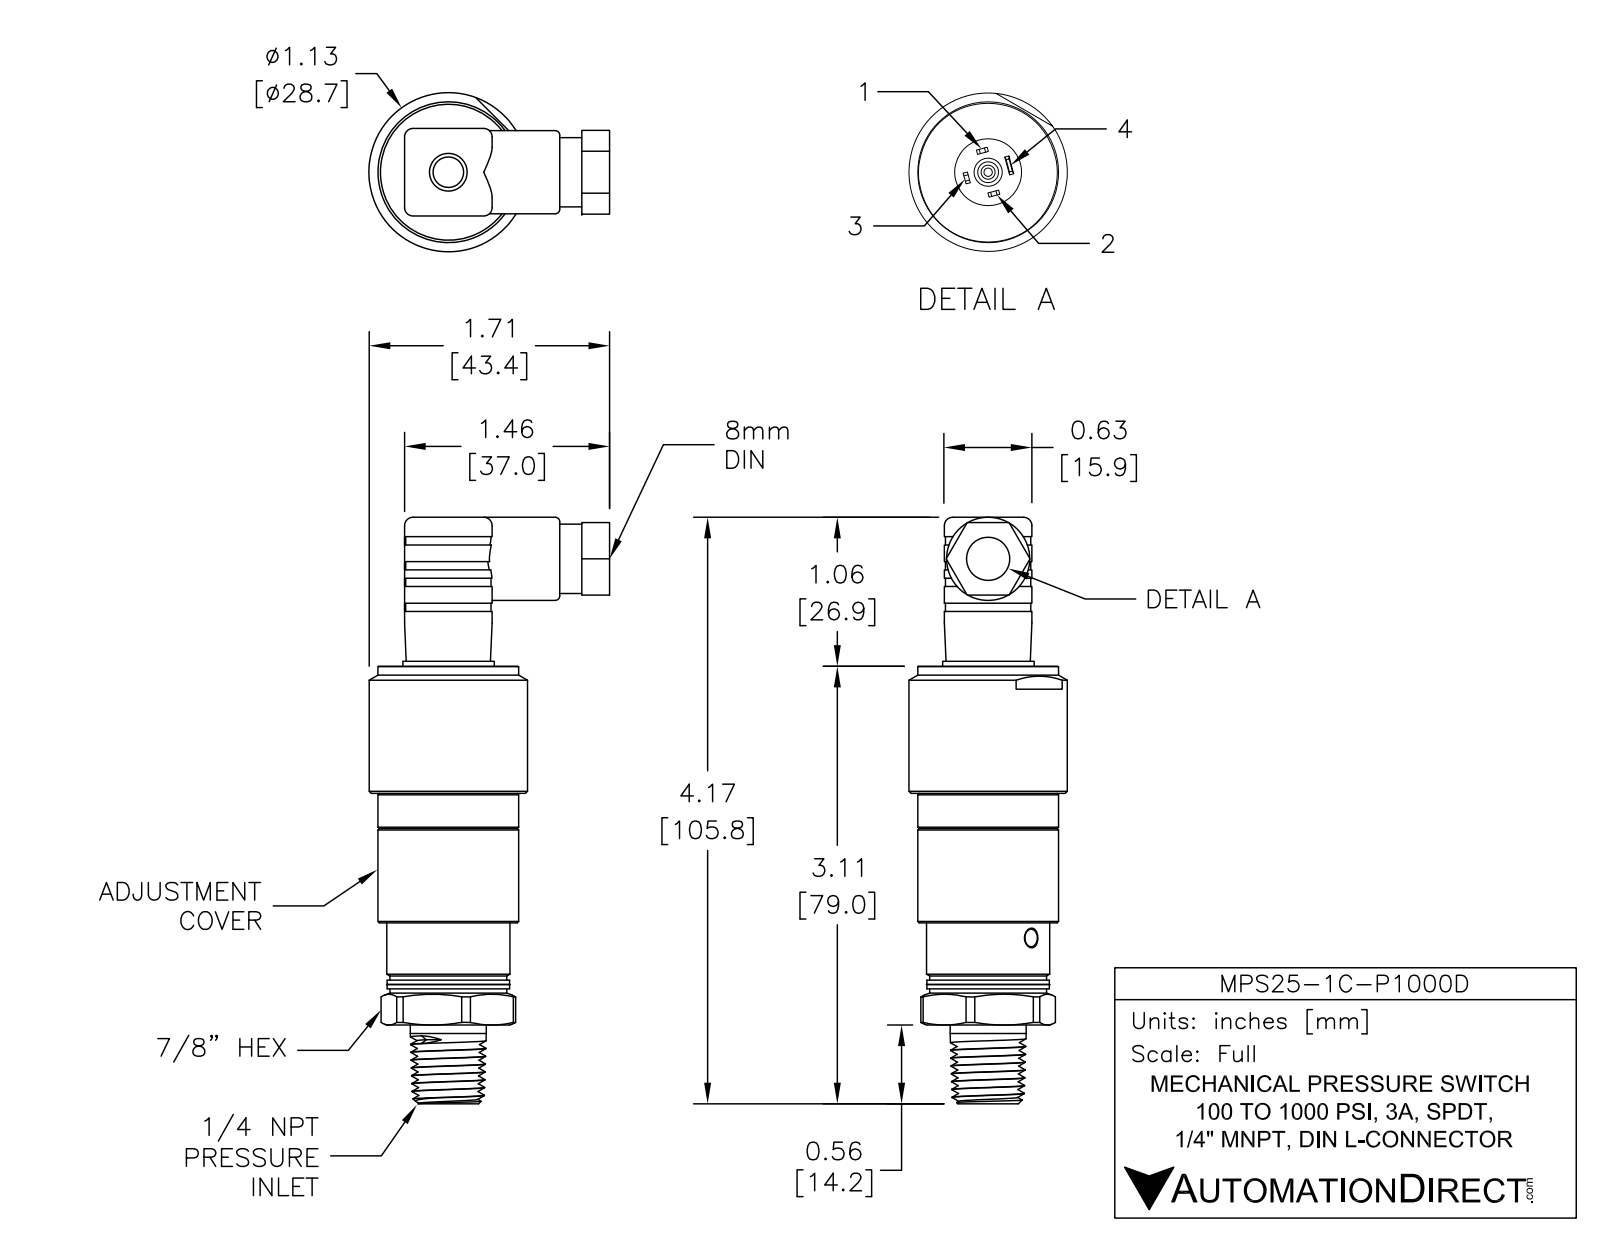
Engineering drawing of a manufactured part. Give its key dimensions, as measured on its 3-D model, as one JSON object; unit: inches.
{"part_name": "MPS25-1C-D100D", "step_written_by": "SolidWorks 2017 (AUTOMOTIVE_DESIGN)", "units": "inches", "bodies": {"solids": 11, "faces": 1424, "planar": 608, "cylindrical": 448, "other": 368}, "overall_size": [4.172, 1.596, 1.565], "volume_in3": 1.849, "surface_area_in2": 39.21, "round_holes": [[0.025, 4], [0.841, 2], [0.88, 2], [0.094, 1], [0.096, 1], [0.106, 1], [0.109, 1], [0.111, 1], [0.12, 1], [0.197, 1], [0.2, 1], [0.222, 1]], "round_bosses_or_shafts": [[0.062, 2], [1.125, 1], [1, 1], [0.987, 1], [0.875, 1], [0.87, 1], [0.837, 1], [0.83, 1]], "partial_cylinders_radius": [[0.01, 24], [0.059, 8], [0.039, 4], [0.051, 4], [0.06, 4], [0.091, 4], [0.197, 4], [0.006, 3]], "face_to_face_distances": [0.291, 0.992, 0.287, 0.289, 0.035, 0.043, 0.579, 0.622, 0.612, 0.903], "hole_center_spacings": [0.902]}
